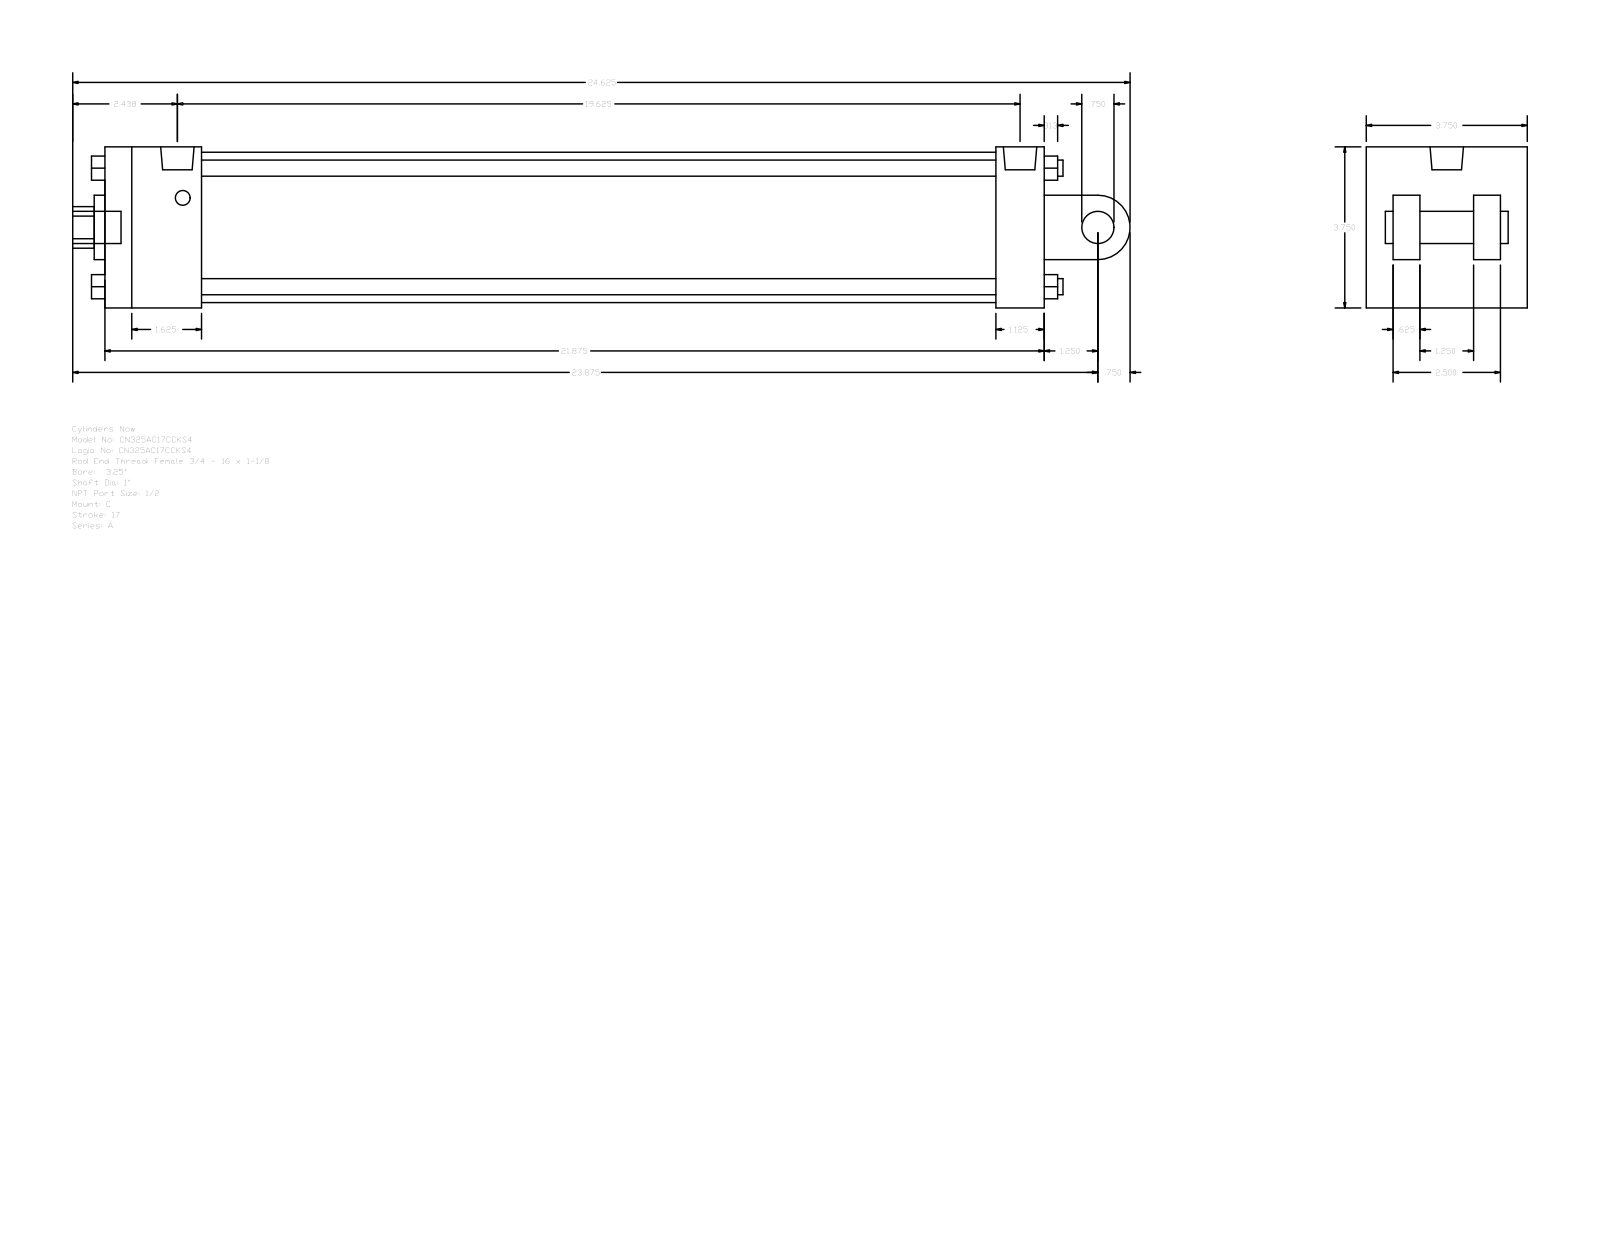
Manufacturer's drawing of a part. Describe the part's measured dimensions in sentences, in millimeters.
The part is named "A_C__0325_1". Its 3-D file was written by "GSSL Pune (CONFIG_CONTROL_DESIGN)". It is 0 solids with 135 faces: 102 planar, 33 cylindrical and 0 other. Overall it measures 625.48 by 95.25 by 95.25 millimeters. Round holes: 2 of diameter 8.73, 1 of diameter 19.77, 1 of diameter 25.4, 1 of diameter 38.1, 1 of diameter 88.9. Round bosses or shafts: 4 of diameter 9.53, 2 of diameter 19.05, 2 of diameter 8.73, 1 of diameter 19.77. Partial cylindrical surfaces (rounded edges, fillets, slot ends): 1 of radius 12.29, 1 of radius 19.05. The main face-to-face distances are 95.24, 555.62, 15.87, 63.5, 28.57, 47.63, 31.74, 79.37, 66.67, 527.05. The hole center spacings are 3.18.
